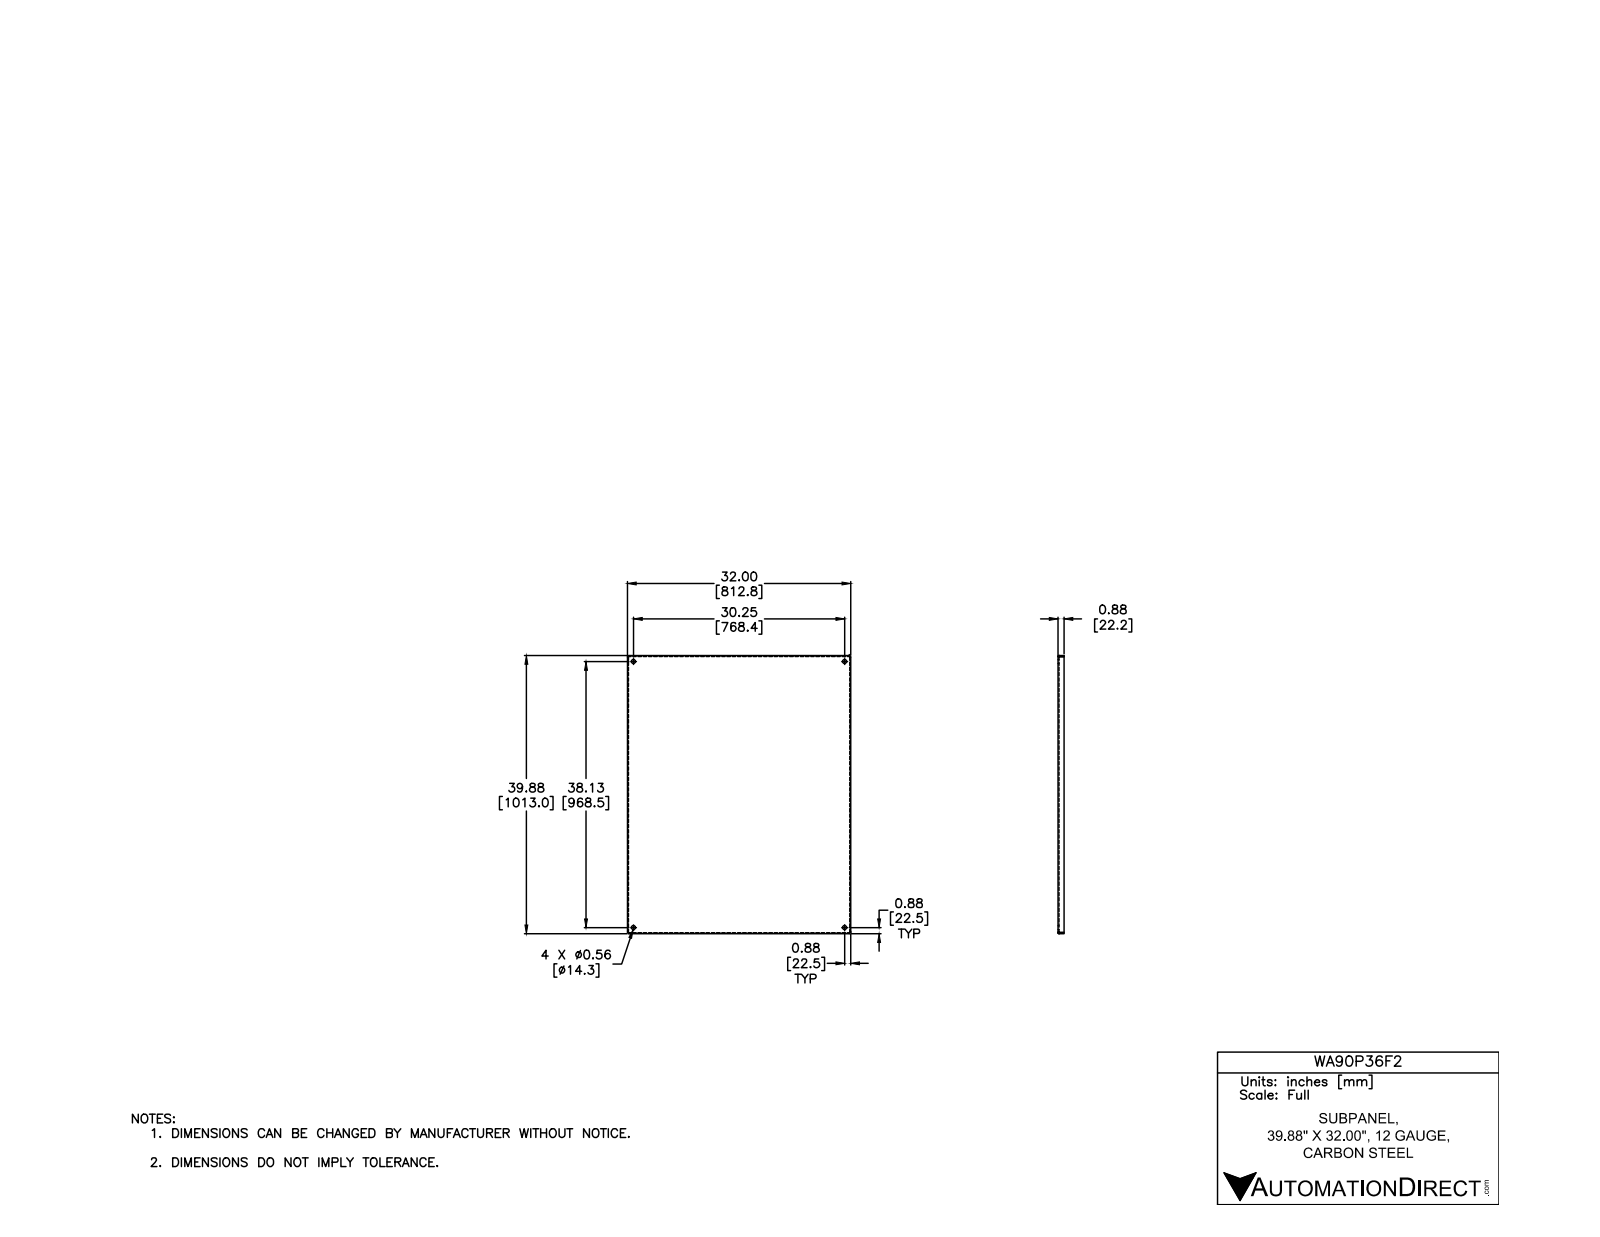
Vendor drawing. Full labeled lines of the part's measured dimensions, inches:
Part name (STEP PRODUCT): WA_P_F
STEP written by: Autodesk Inventor 2012 (AUTOMOTIVE_DESIGN)
Units: inches
Bodies: 1 solid, 42 faces (22 planar, 12 cylindrical, 8 other)
Overall size (bounding box): 39.888 × 32 × 0.875
Volume: 129.6 in³ · Surface area: 2 778 in²
Round holes (diameter × count): ⌀0.563 ×4
Partial cylindrical surfaces — rounded edges, fillets, slot ends (radius × count): R0.031 ×4, R0.125 ×4
Main face-to-face distances: 0.094, 31.906, 32, 31.813, 0.094, 39.794, 39.888, 39.7, 39.794, 0.781
Hole centre spacings: 30.25, 38.138, 48.678
